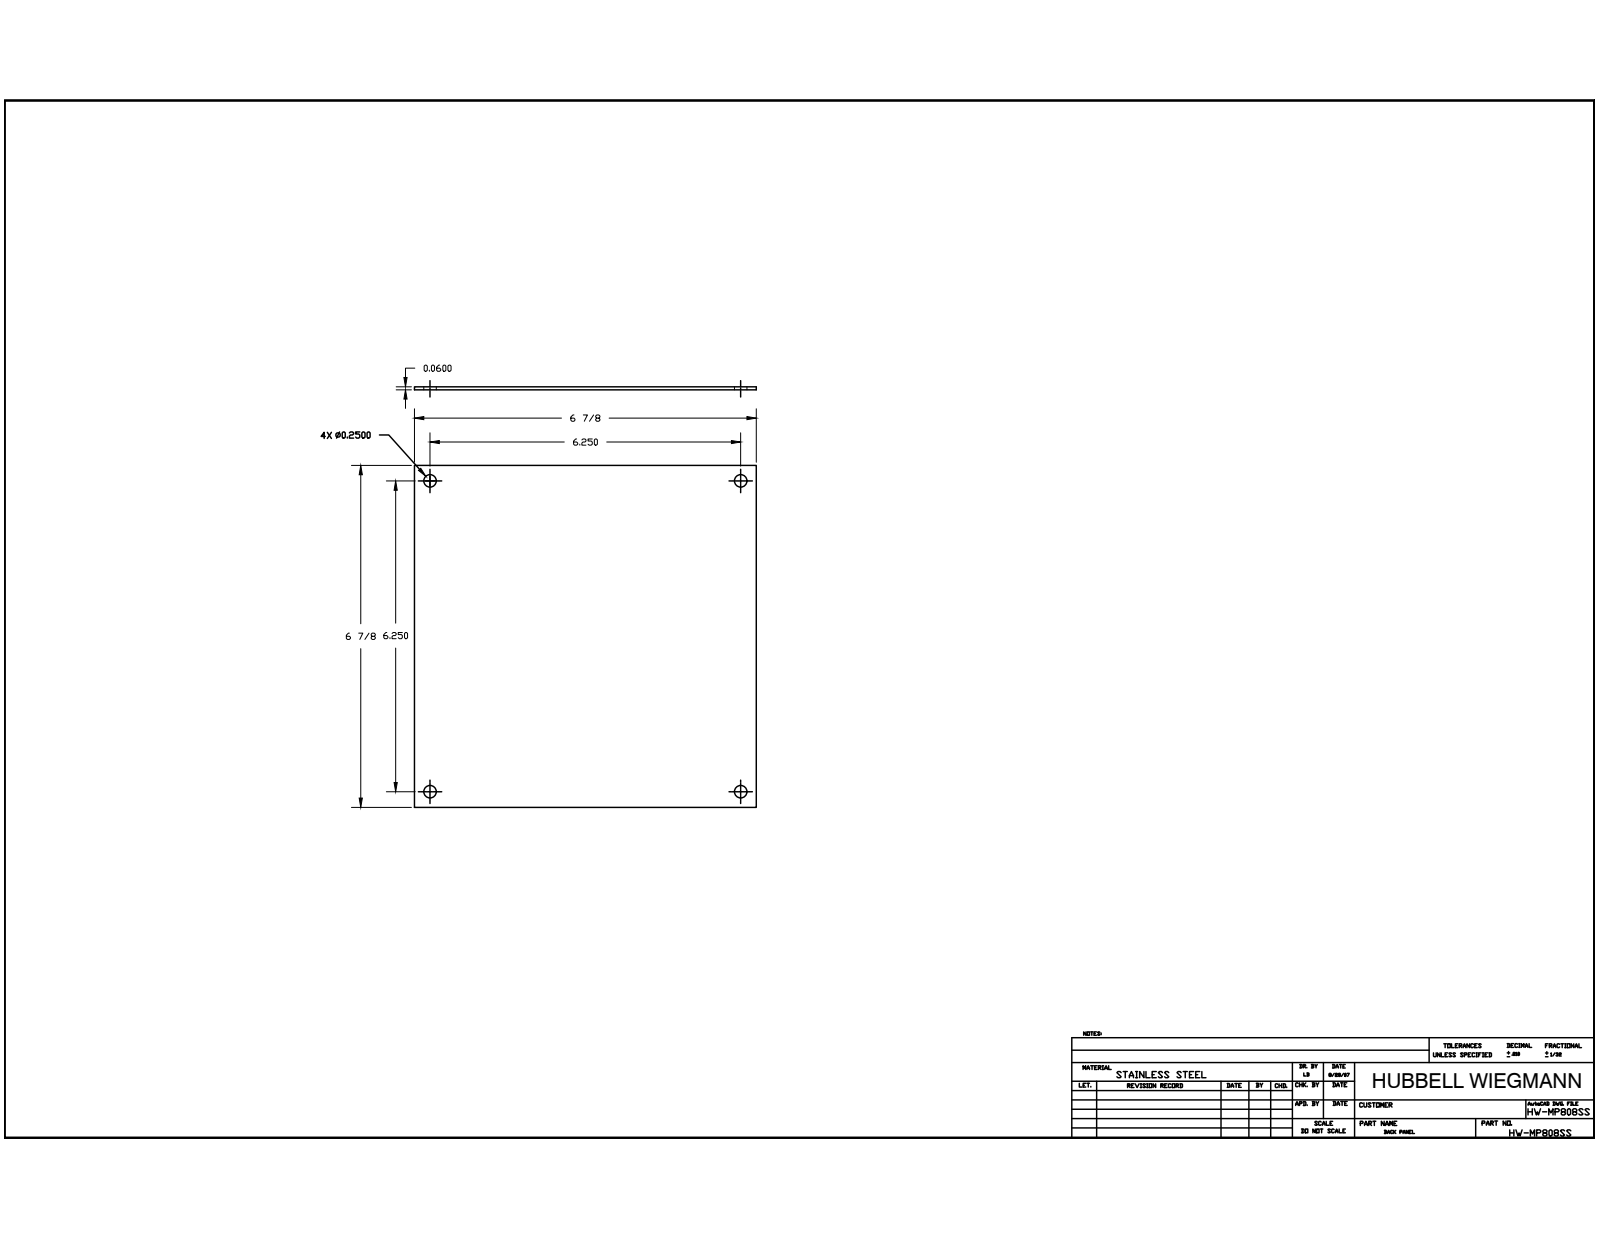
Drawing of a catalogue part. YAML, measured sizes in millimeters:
part_name: "BP88SS_STP"
step_written_by: "Autodesk Inventor 2014 (AUTOMOTIVE_DESIGN)"
units: millimeters
bodies: {solids: 1, faces: 10, planar: 6, cylindrical: 4, other: 0}
overall_size: [174.62, 174.62, 1.52]
volume: 46280
surface_area: 61921
round_holes:
  - {diameter: 6.35, count: 4}
face_to_face_distances: [1.52, 174.62]
hole_center_spacings: [158.76, 224.52]
